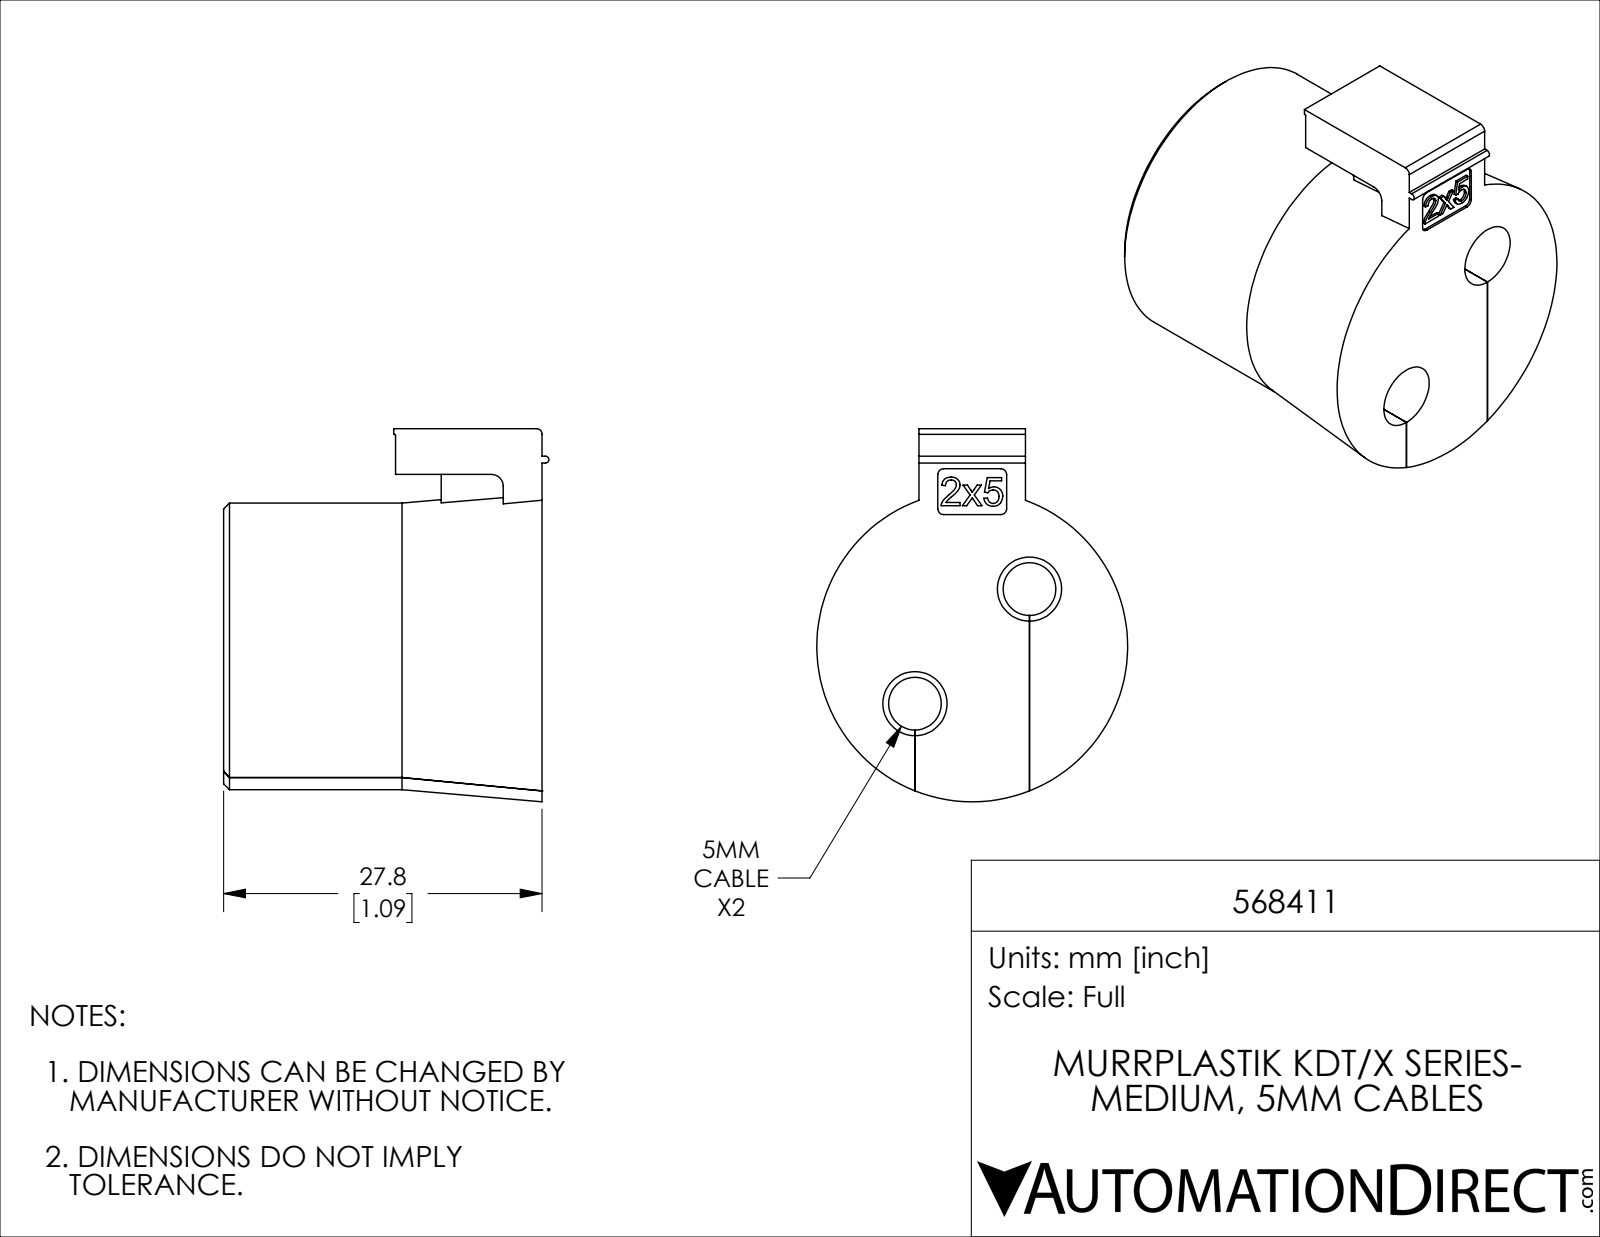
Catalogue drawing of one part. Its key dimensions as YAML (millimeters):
part_name: "568411"
step_written_by: "SolidWorks 2019 (CONFIG_CONTROL_DESIGN)"
units: millimeters
bodies: {solids: 1, faces: 117, planar: 53, cylindrical: 27, other: 37}
overall_size: [32.6, 28.4, 27.2]
volume: 13400
surface_area: 5544
round_holes:
  - {diameter: 4.6, count: 2}
  - {diameter: 5.6, count: 2}
round_bosses_or_shafts:
  - {diameter: 25, count: 1}
partial_cylinders:
  - {radius: 0.5, count: 5}
  - {radius: 0.1, count: 1}
  - {radius: 0.3, count: 1}
  - {radius: 1, count: 1}
face_to_face_distances: [27.8, 10, 0.4, 9.7, 10, 10, 4, 0.4, 9.7, 0.3]
hole_center_spacings: [14.1]
